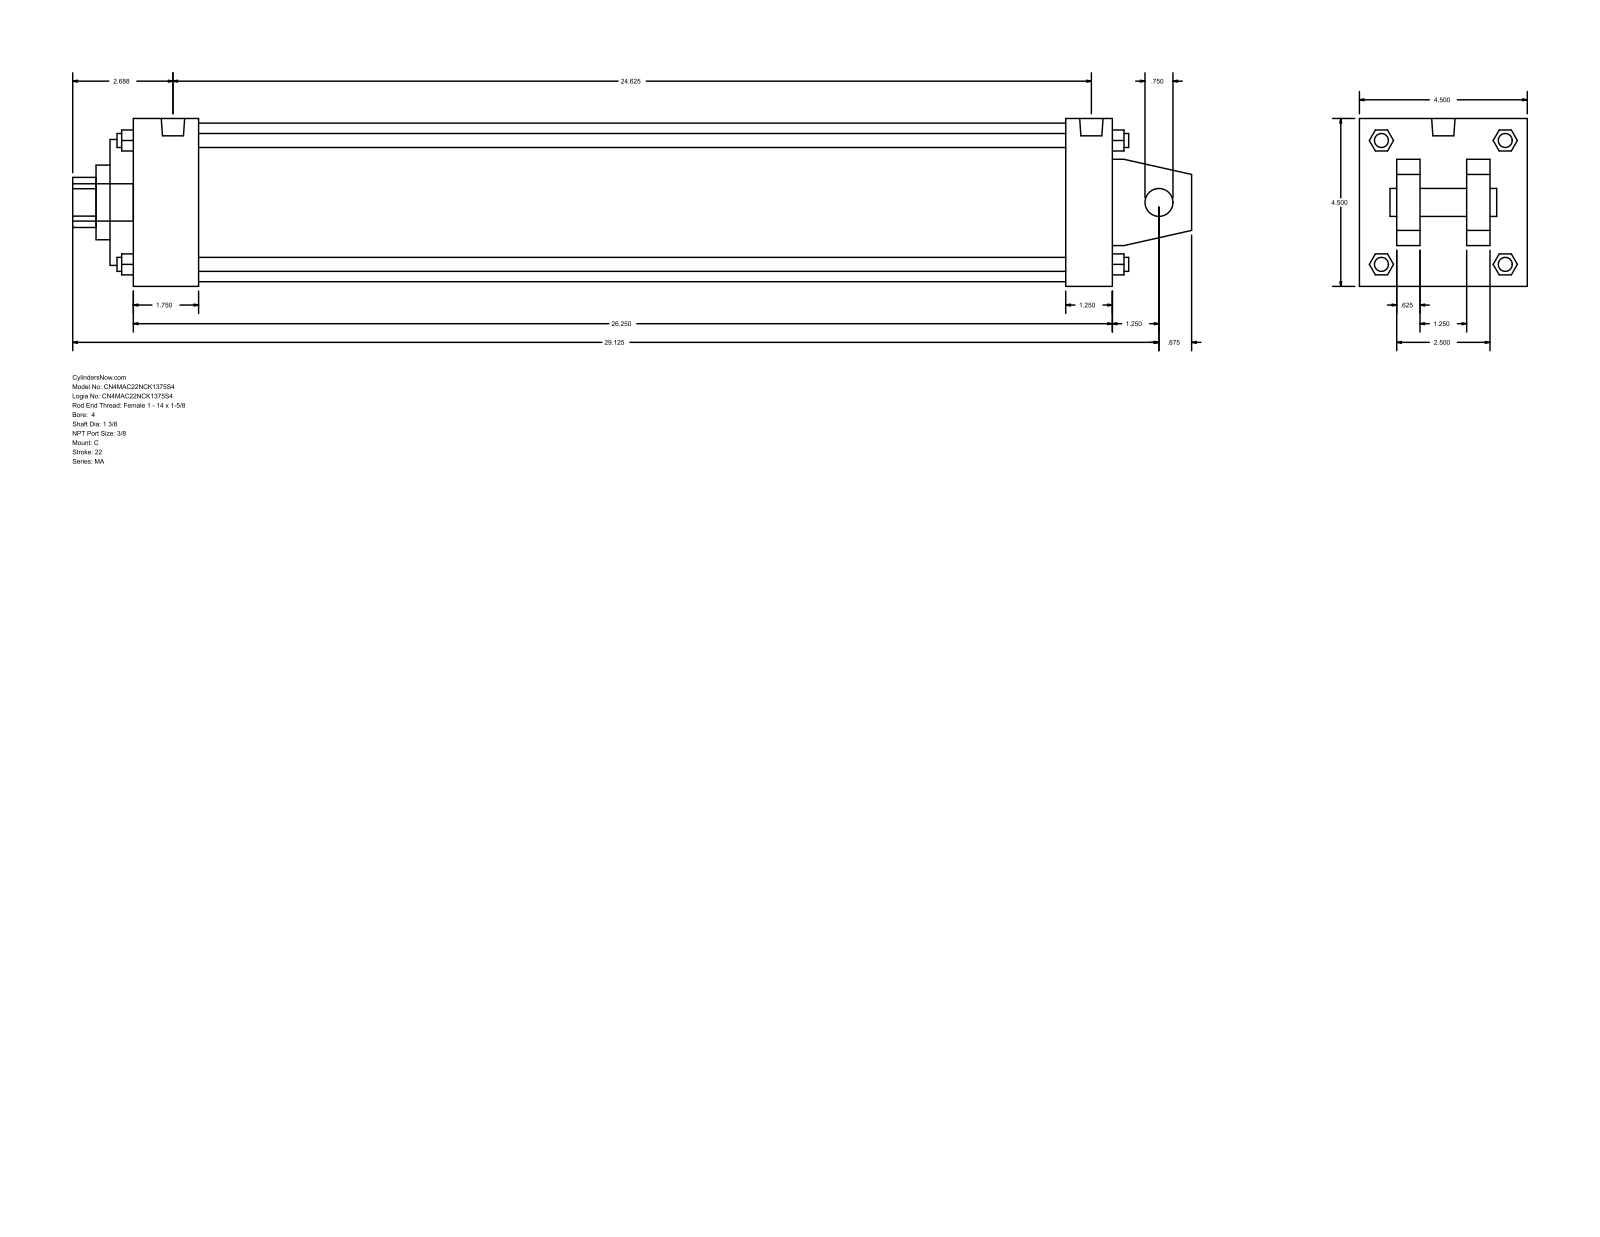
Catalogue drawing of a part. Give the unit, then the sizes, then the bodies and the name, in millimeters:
Units: millimetres
Overall size (bounding box): 762 × 114.3 × 114.3
Round holes (diameter × count): ⌀19.05 ×1, ⌀34.92 ×1, ⌀50.8 ×1, ⌀85.72 ×1, ⌀107.95 ×1
Round bosses / shafts (diameter × count): ⌀11.11 ×4, ⌀9.53 ×4, ⌀15.93 ×2, ⌀25.4 ×1
Partial cylindrical surfaces — rounded edges, fillets, slot ends (radius × count): R17.06 ×1
Main face-to-face distances: 114.3, 15.87, 666.75, 73.03, 41.27, 25.4, 88.9, 47.63, 682.62, 650.87
Bodies: 0 solids, 141 faces (109 planar, 32 cylindrical, 0 other)
Part name (STEP PRODUCT): MA_C__0400_1.375
STEP written by: GSSL Pune (CONFIG_CONTROL_DESIGN)
